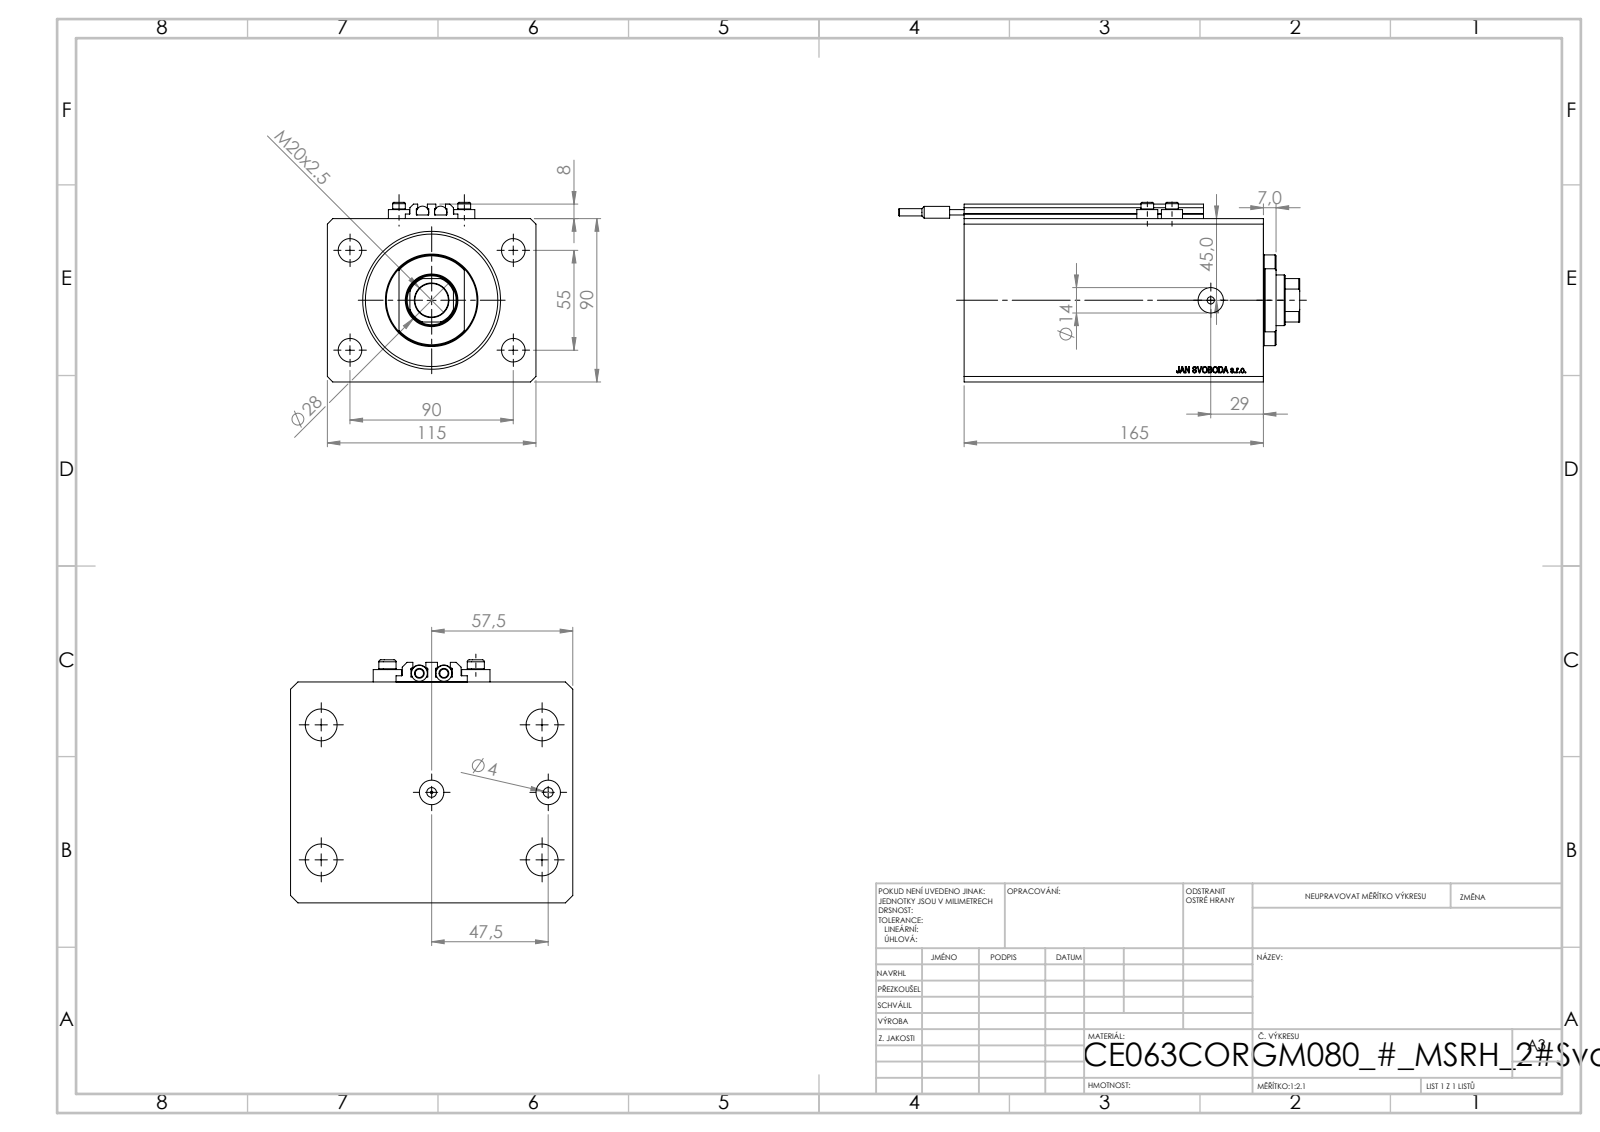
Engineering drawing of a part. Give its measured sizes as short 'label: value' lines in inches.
name: V250CE_C_Body; V250CE_C_VCP; ALLEN BOLT V250CE; V250CE_VC_C (+1 more)
written by: SolidWorks 2019 (CONFIG_CONTROL_DESIGN)
unit: in
bodies: 10 solids, 1090 faces (536 planar, 100 cylindrical, 454 other)
size: 8.701 × 4.528 × 3.898
volume: 88.18 in³; area: 322.6 in²
holes: 8× ⌀0.157, 4× ⌀0.512, 2× ⌀0.394, 2× ⌀0.551, 1× ⌀0.049, 1× ⌀0.728, 1× ⌀1.102, 1× ⌀2.48, 1× ⌀2.992
bosses: 4× ⌀0.457, 4× ⌀0.276, 2× ⌀0.268, 2× ⌀0.256, 2× ⌀0.157, 1× ⌀1.969
rounds: 10× R0.008, 1× R0.531
face distances: 3.543, 4.528, 6.496, 0.705, 5.791, 0.787, 5.709, 5.004, 2.559, 3.937
hole spacings: 2.076, 0.535, 1.087, 1.417, 1.515, 2.165, 3.543, 3.799
